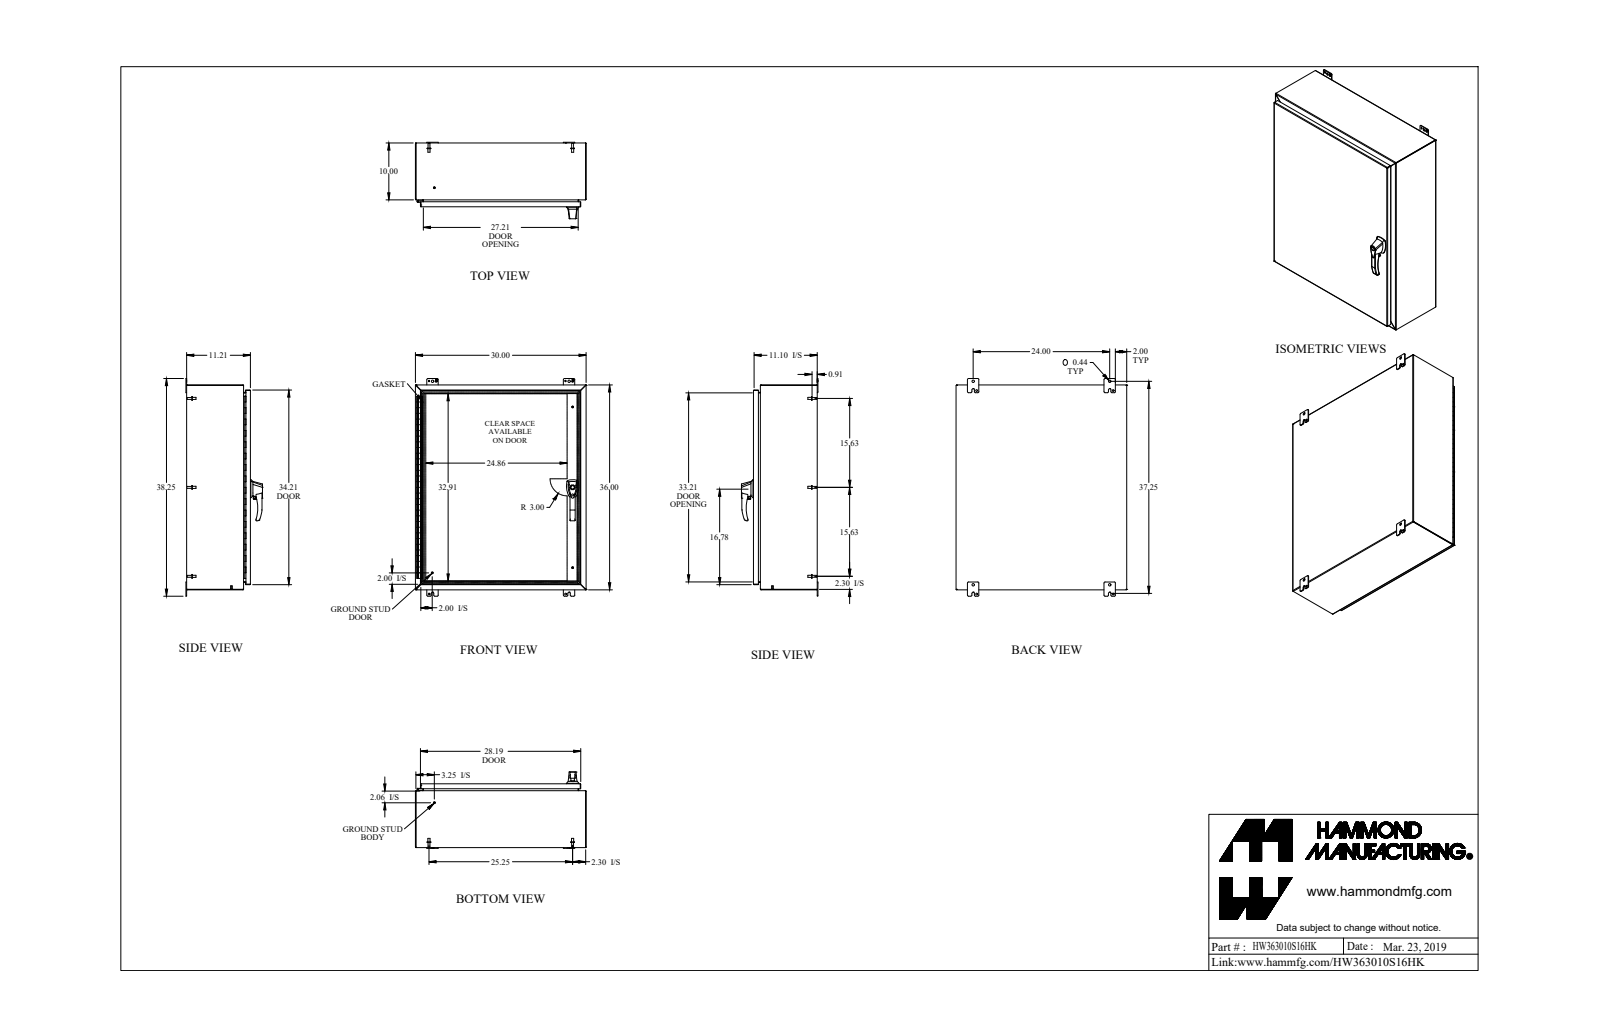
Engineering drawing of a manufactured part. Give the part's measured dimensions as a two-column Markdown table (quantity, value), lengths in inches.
| quantity | value |
| --- | --- |
| part name | HW363010S16HK |
| STEP written by | SolidWorks 2018 (AUTOMOTIVE_DESIGN) |
| units | inches |
| bodies | 44 solids, 1542 faces (720 planar, 658 cylindrical, 164 other) |
| overall size | 38.25 × 30 × 13.45 |
| volume | 312.1 in³ |
| surface area | 8 240 in² |
| round holes (diameter × count) | 0.176 × 6, 0.313 × 5, 0.25 × 3, 0.265 × 3, 0.413 × 3, 0.196 × 2, 0.256 × 2, 0.394 × 2, 0.437 × 2, 0.11 × 1, 0.233 × 1, 0.33 × 1 |
| round bosses / shafts (diameter × count) | 0.375 × 11, 0.25 × 7, 0.65 × 6, 0.332 × 6, 0.156 × 6, 0.313 × 4, 1 × 3, 0.51 × 3 |
| partial cylindrical surfaces (radius × count) | 0.25 × 27, 0.188 × 24, 0.036 × 20, 0.108 × 20, 0.06 × 12, 0.125 × 9, 0.045 × 8, 0.218 × 8 |
| main face-to-face distances | 0.072, 11.138, 11.066, 11.138, 11.21, 0.072, 29.928, 35.928, 29.856, 30 |
| hole center spacings | 1.111, 14.118, 14.119, 28.237, 1.338, 12.78, 14.119, 15.457 |
